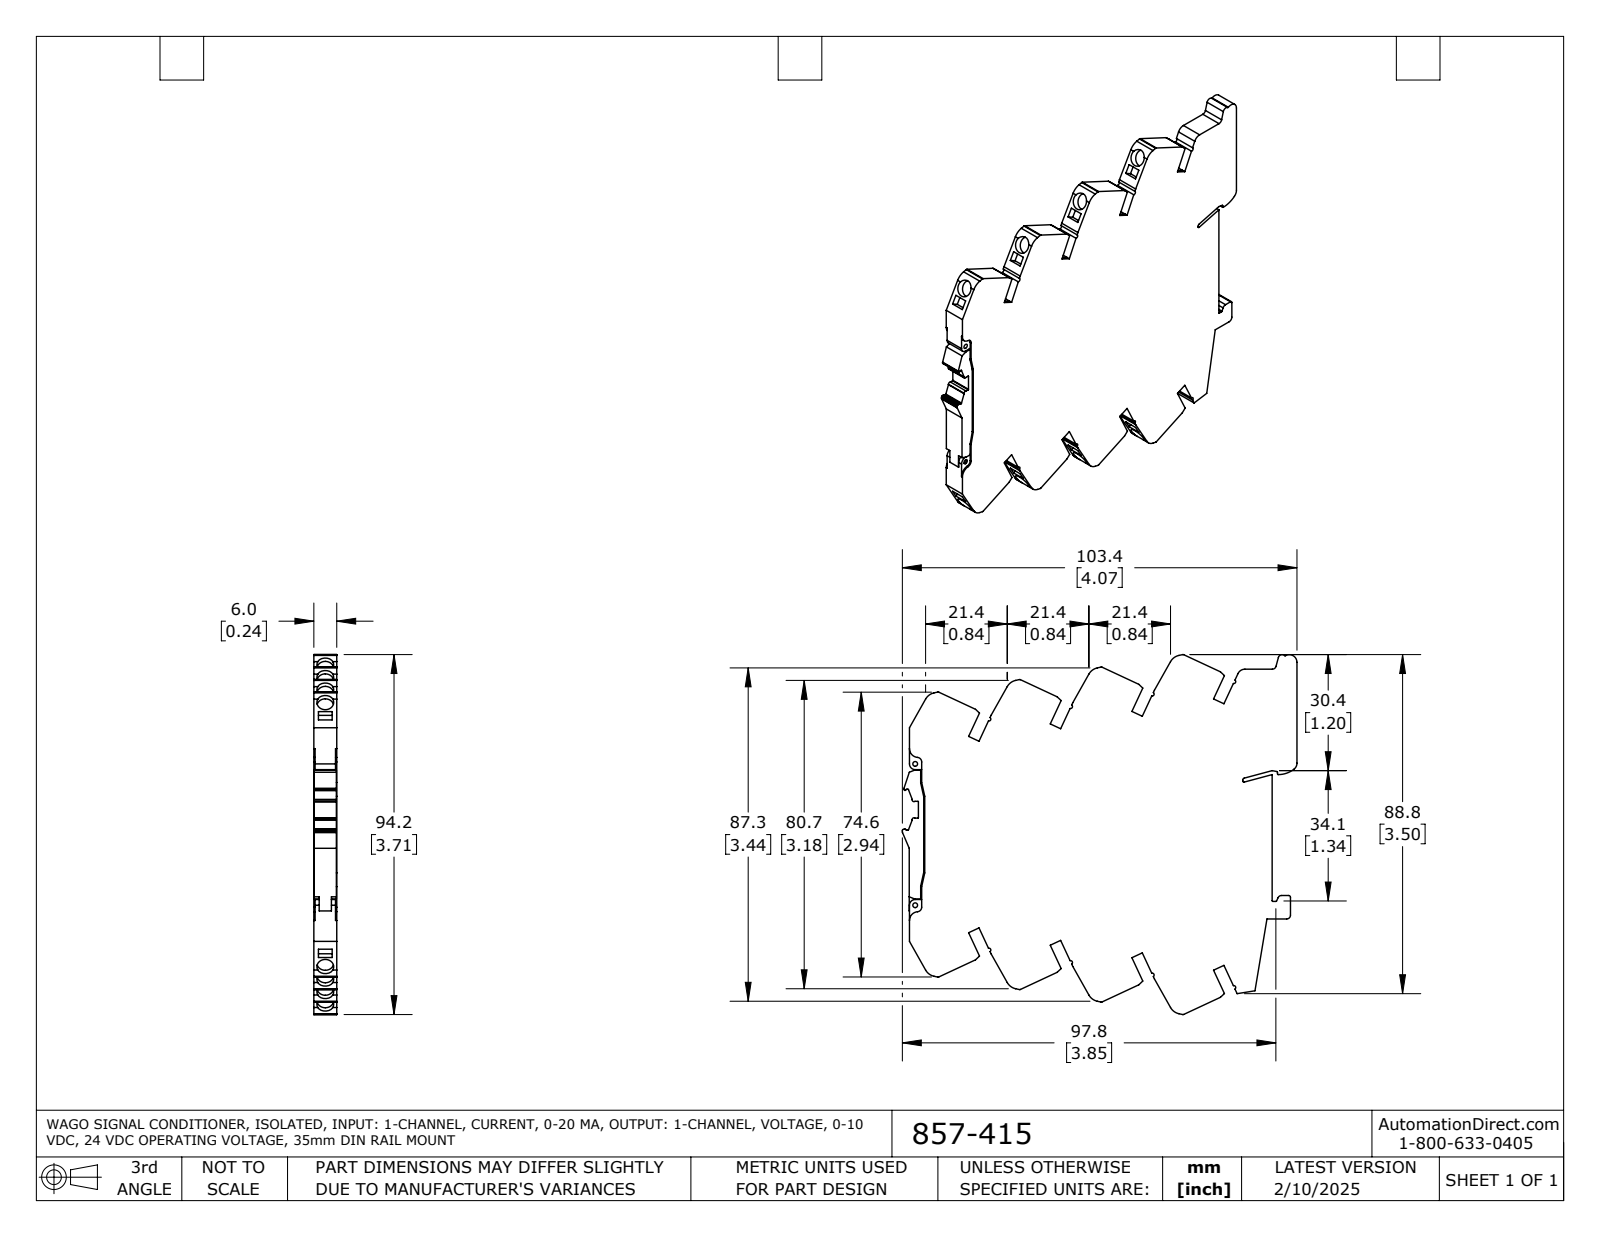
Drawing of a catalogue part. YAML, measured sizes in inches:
part_name: "857-415"
step_written_by: "SolidWorks 2021 (AUTOMOTIVE_DESIGN)"
units: inches
bodies: {solids: 1, faces: 317, planar: 219, cylindrical: 98, other: 0}
overall_size: [4.069, 3.711, 0.236]
volume: 2.681
surface_area: 29.86
round_holes:
  - {diameter: 0.173, count: 8}
  - {diameter: 0.049, count: 2}
partial_cylinders:
  - {radius: 0.02, count: 12}
  - {radius: 0.008, count: 11}
  - {radius: 0.016, count: 8}
  - {radius: 0.132, count: 8}
  - {radius: 0.039, count: 4}
  - {radius: 0.012, count: 3}
  - {radius: 0.079, count: 3}
  - {radius: 0.018, count: 2}
face_to_face_distances: [0.236, 0.708, 0.67, 0.473, 0.232, 0.472, 0.118, 0.945, 1.417, 0.256]
hole_center_spacings: [0.526, 0.525, 1.051, 1.051, 1.052, 1.457, 1.576, 1.577]
